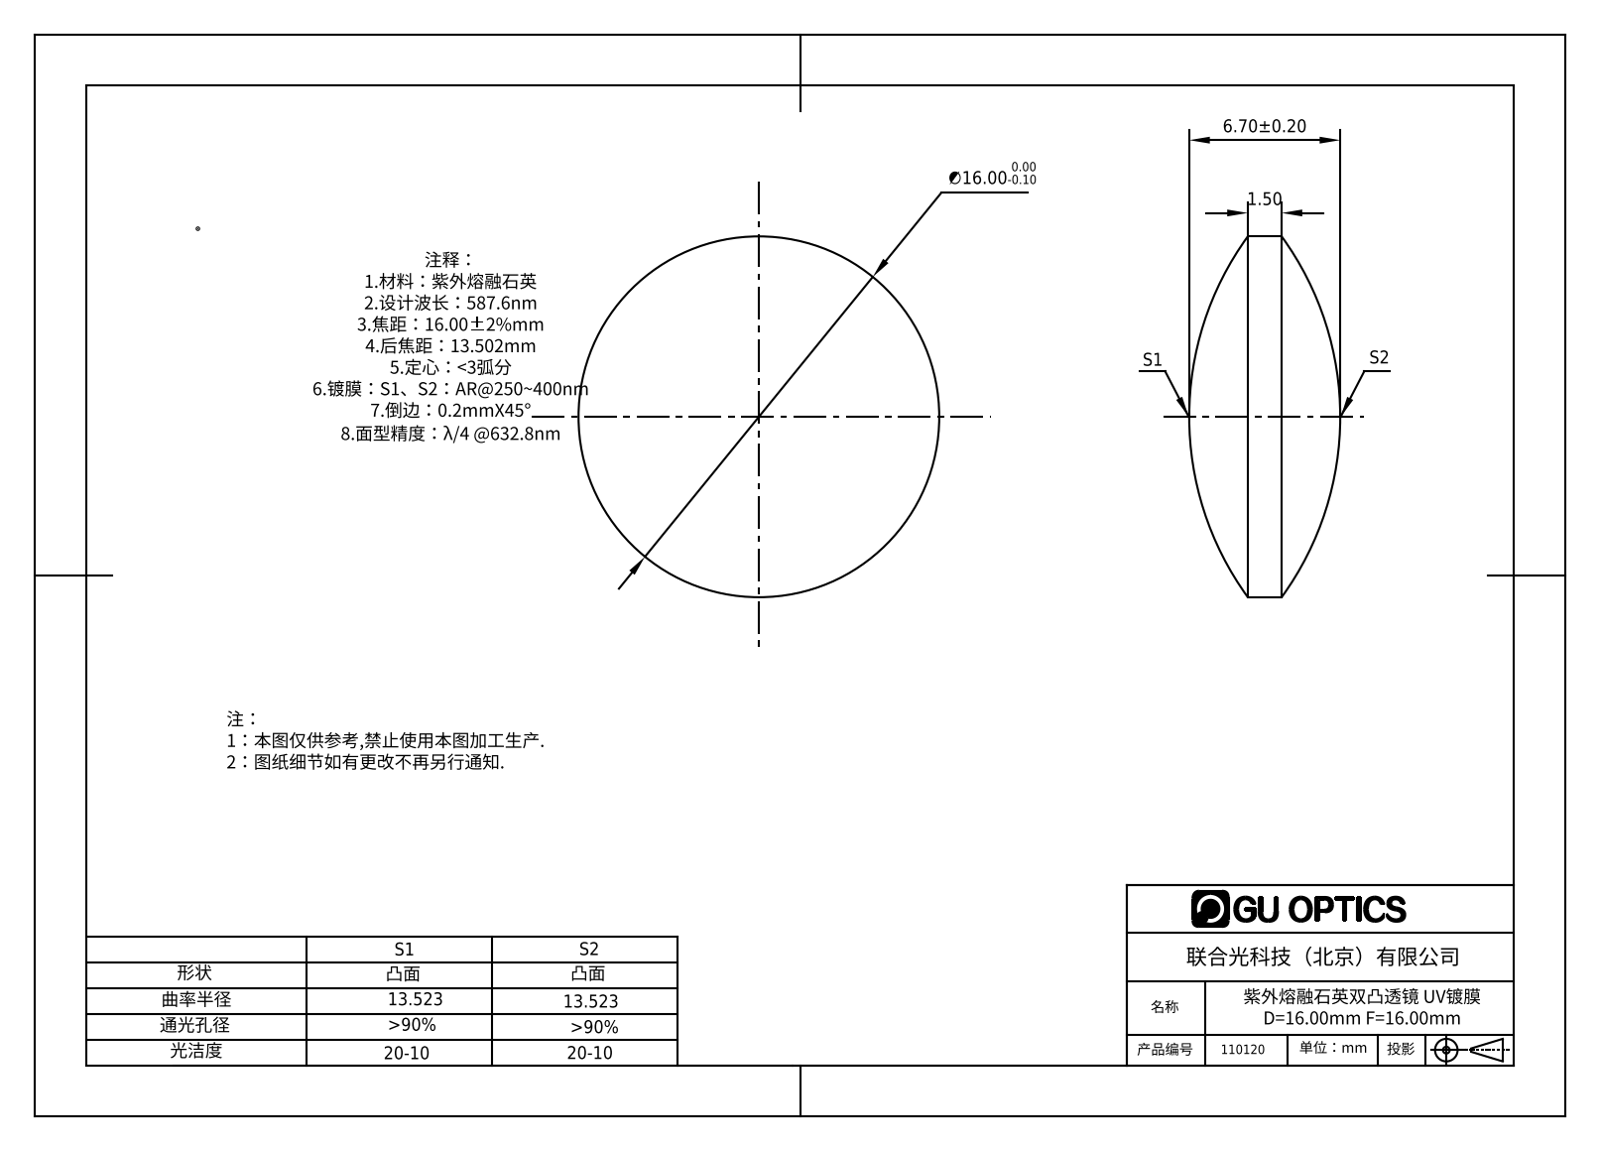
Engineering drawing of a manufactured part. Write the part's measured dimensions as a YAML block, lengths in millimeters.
part_name: "110096"
step_written_by: "SolidWorks 2016 (CONFIG_CONTROL_DESIGN)"
units: millimeters
bodies: {solids: 1, faces: 6, planar: 0, cylindrical: 2, other: 4}
overall_size: [16, 16, 6.7]
volume: 843
surface_area: 520
round_bosses_or_shafts:
  - {diameter: 16, count: 1}
